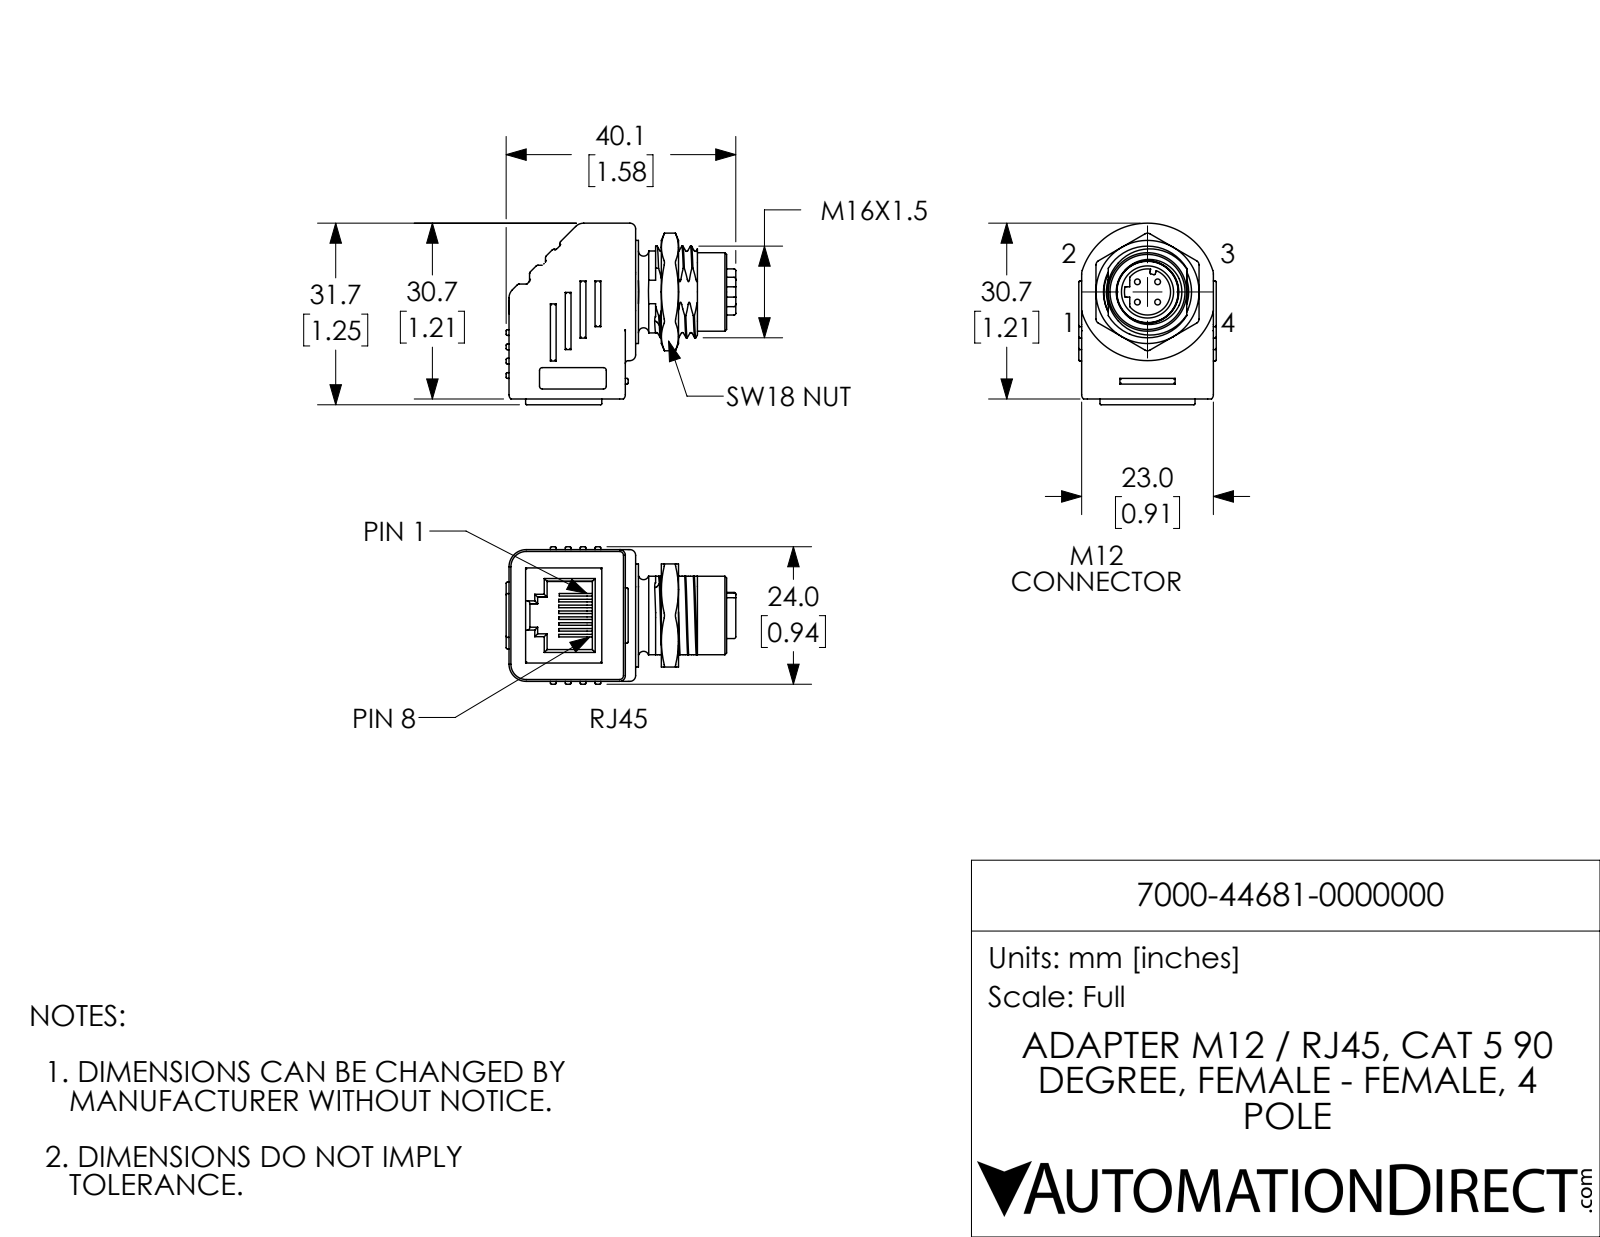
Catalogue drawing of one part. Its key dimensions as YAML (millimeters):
part_name: "7000-44681-0000000"
step_written_by: "SolidWorks 2017 (AUTOMOTIVE_DESIGN)"
units: millimeters
bodies: {solids: 2, faces: 552, planar: 207, cylindrical: 210, other: 135}
overall_size: [40.1, 31.7, 24]
volume: 14000
surface_area: 6574
round_holes:
  - {diameter: 1, count: 4}
  - {diameter: 7.5, count: 1}
  - {diameter: 7.5, count: 1}
  - {diameter: 9.4, count: 1}
  - {diameter: 10.8, count: 1}
  - {diameter: 10.9, count: 1}
  - {diameter: 14.4, count: 1}
round_bosses_or_shafts:
  - {diameter: 24, count: 1}
  - {diameter: 18, count: 1}
  - {diameter: 14.3, count: 1}
  - {diameter: 13.7, count: 1}
  - {diameter: 10.7, count: 1}
  - {diameter: 10, count: 1}
  - {diameter: 9.4, count: 1}
  - {diameter: 8.1, count: 1}
partial_cylinders:
  - {radius: 0.2, count: 52}
  - {radius: 0.5, count: 11}
  - {radius: 1, count: 10}
  - {radius: 0.3, count: 6}
  - {radius: 0.8, count: 6}
  - {radius: 2, count: 4}
  - {radius: 0.4, count: 2}
  - {radius: 0.7, count: 2}
face_to_face_distances: [23, 3, 5.6, 17.4, 1.8, 22.1, 20.3, 14.6, 5.8, 7.6]
hole_center_spacings: [2.5, 3.5, 5]
